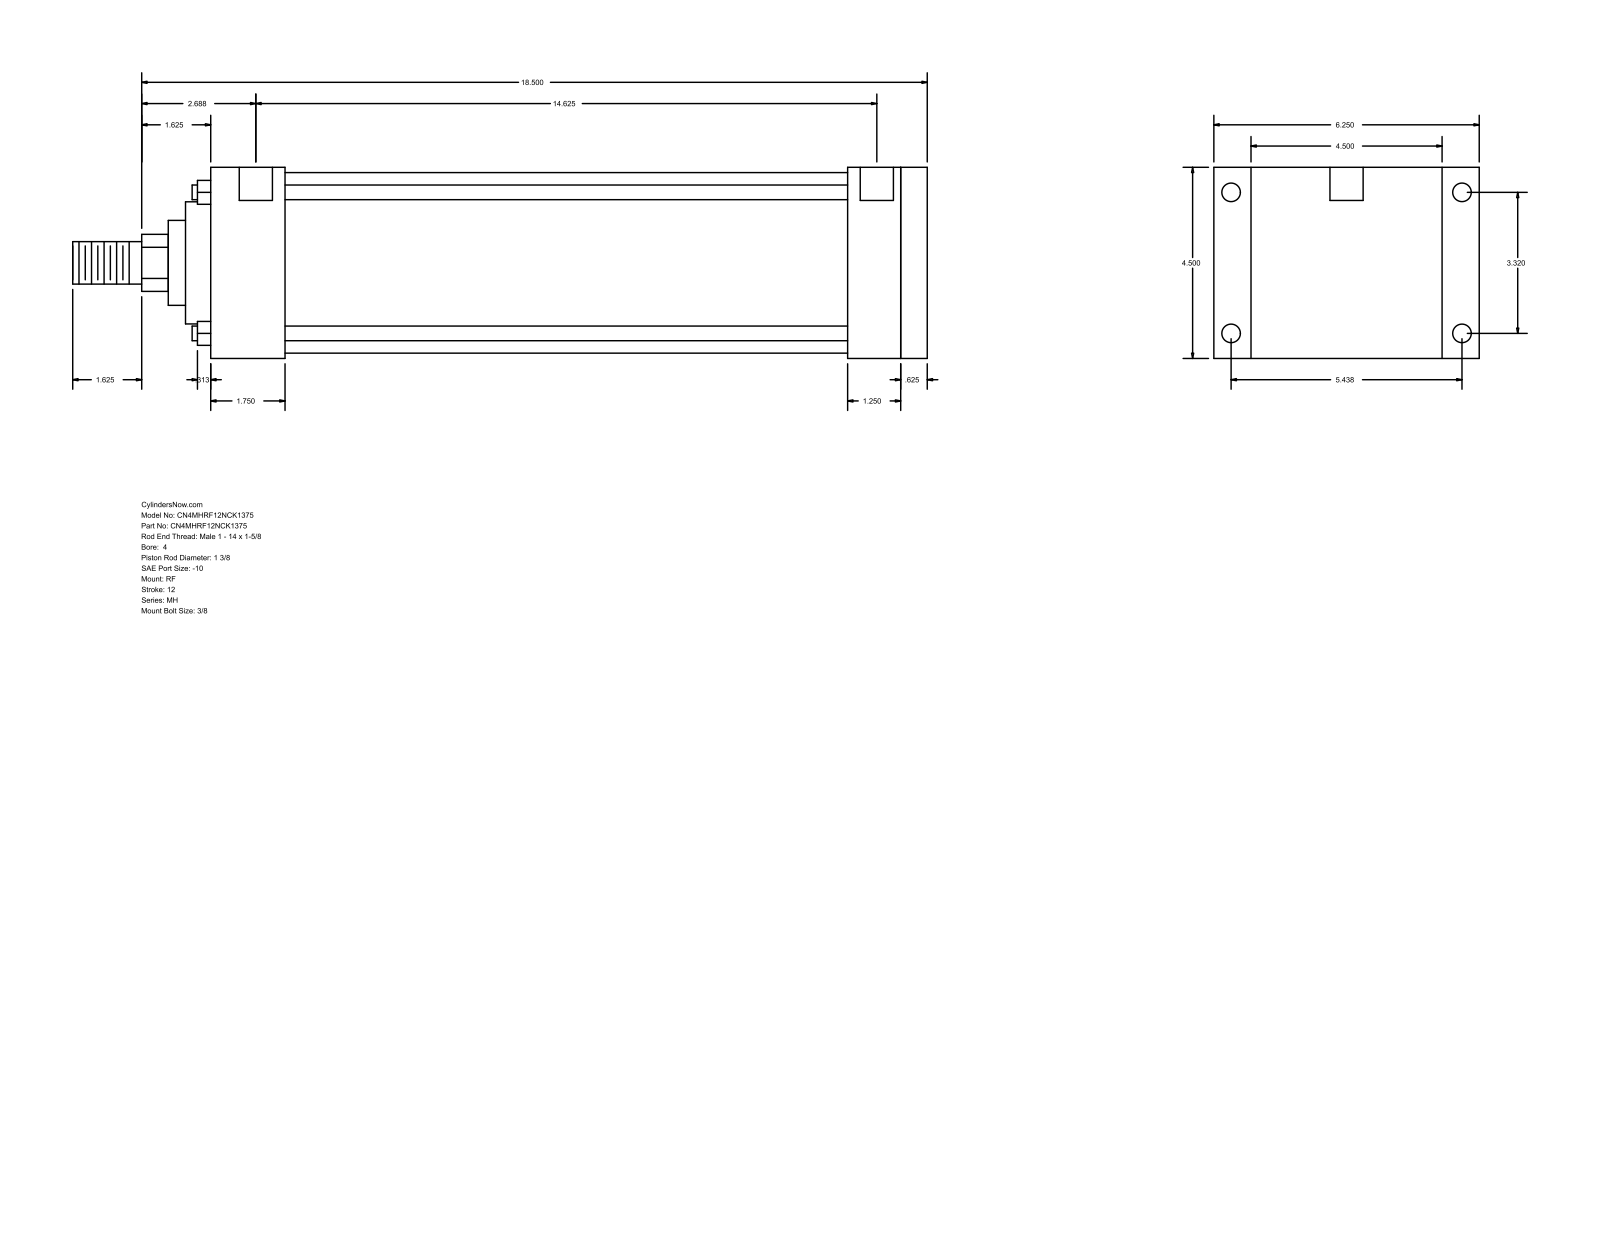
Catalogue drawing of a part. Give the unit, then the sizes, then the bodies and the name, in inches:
Units: inches
Overall size (bounding box): 20.125 × 6.25 × 4.5
Round holes (diameter × count): ⌀0.344 ×4, ⌀0.438 ×4, ⌀0.781 ×2
Round bosses / shafts (diameter × count): ⌀0.345 ×4, ⌀4.25 ×1, ⌀2.875 ×1, ⌀2 ×1, ⌀1.375 ×1, ⌀1 ×1
Partial cylindrical surfaces — rounded edges, fillets, slot ends (radius × count): R0.672 ×1
Main face-to-face distances: 4.5, 16.875, 0.625, 16.25, 1.75, 14.5, 15.125, 15, 13.25, 1.25
Hole centre spacings: 3.32, 5.438, 6.371, 14.75, 0.062, 0.063, 14.625, 14.687
Bodies: 0 solids, 94 faces (65 planar, 29 cylindrical, 0 other)
Part name (STEP PRODUCT): MH_RF__0400_1.375
STEP written by: GSSL Pune (CONFIG_CONTROL_DESIGN)
